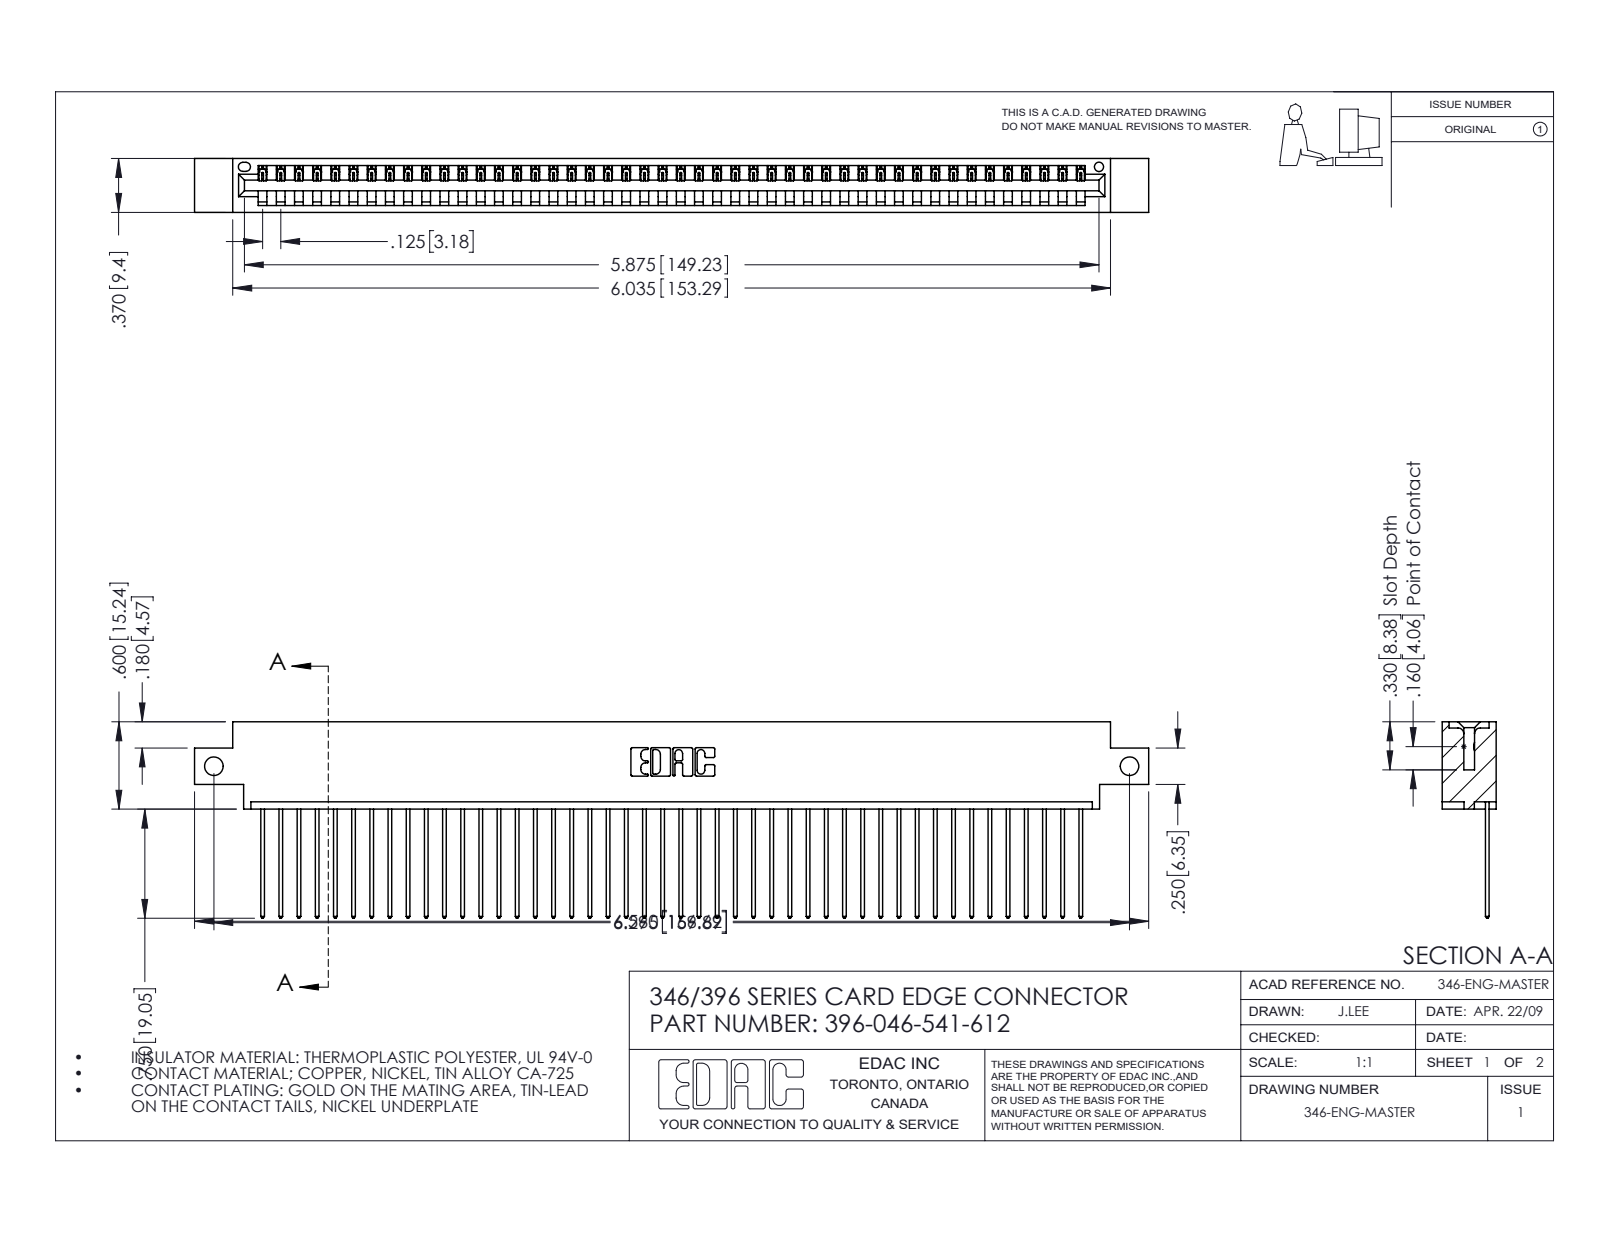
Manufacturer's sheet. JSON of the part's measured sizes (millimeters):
{"part_name": "345-292-001_345-293-141; 346 Part_0.170 Offset - Side Mount; 396-046-541-612", "step_written_by": "SolidWorks 2016 (CONFIG_CONTROL_DESIGN)", "units": "millimeters", "bodies": {"solids": 47, "faces": 2794, "planar": 1920, "cylindrical": 874, "other": 0}, "overall_size": [166.6, 34.3, 9.4], "volume_mm3": 15900, "surface_area_mm2": 20820, "round_holes": [[3.3, 2], [1.6, 1]], "partial_cylinders_radius": [[0.2, 92], [0.3, 92], [0.3, 22], [0.2, 6], [0.8, 6], [0.7, 3], [0.8, 2], [1, 2]], "face_to_face_distances": [1.2, 8.2, 9.4, 6.4, 1.8, 7.6, 0.6, 3.8, 5.6, 2.5], "hole_center_spacings": [159.9]}
